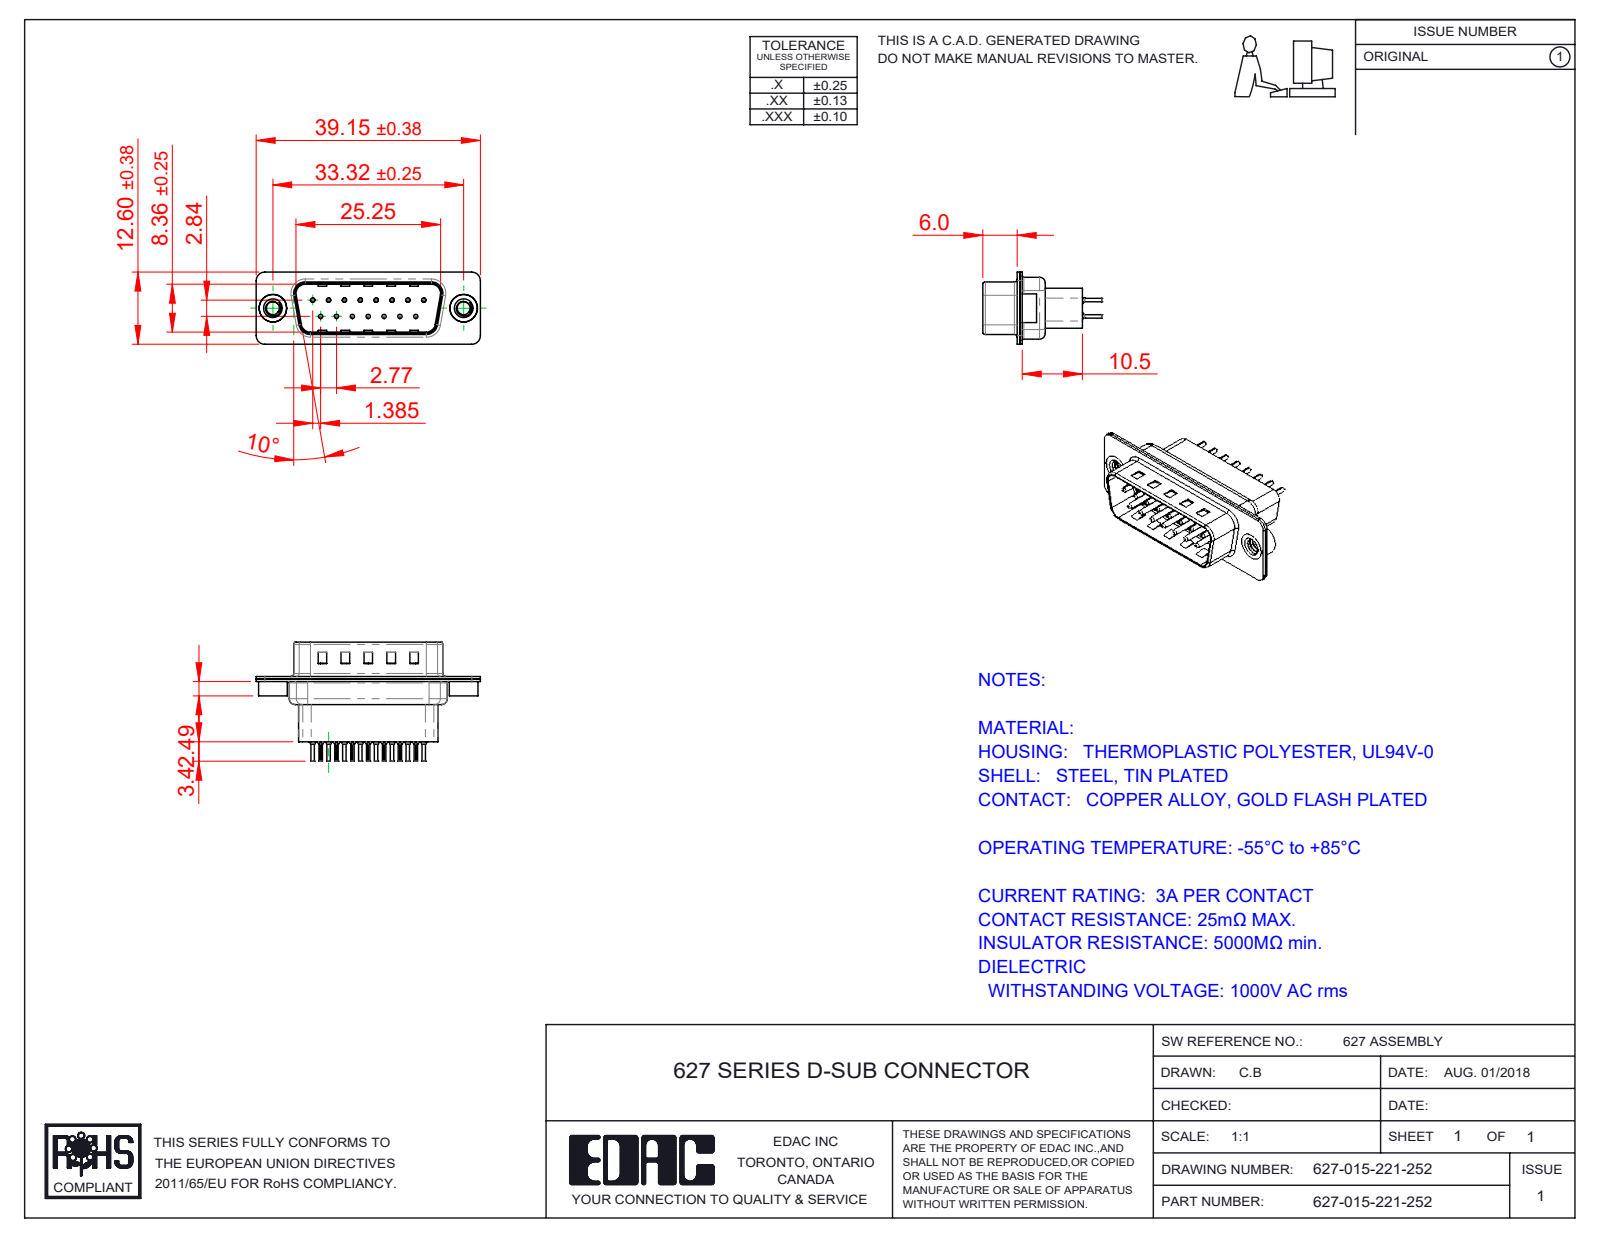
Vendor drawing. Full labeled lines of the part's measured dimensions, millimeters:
Part name (STEP PRODUCT): 627 Contact Row 1_21H; 627 Shell Rear_15 Contacts; 627 4-40 Threaded Rivet; 627 Contact Row 2_21H (+3 more)
STEP written by: SolidWorks 2020 (CONFIG_CONTROL_DESIGN)
Units: millimetres
Bodies: 20 solids, 1806 faces (499 planar, 686 cylindrical, 621 other)
Overall size (bounding box): 39.15 × 20.8 × 12.6
Volume: 2 534 mm³ · Surface area: 6 600 mm²
Round holes (diameter × count): ⌀0.2 ×15, ⌀0.35 ×15, ⌀1.1 ×15, ⌀1.6 ×15, ⌀2.26 ×2, ⌀4 ×2, ⌀4.8 ×2
Round bosses / shafts (diameter × count): ⌀2 ×15, ⌀1.5 ×15, ⌀0.75 ×15, ⌀0.6 ×15, ⌀5 ×2, ⌀4.9 ×2
Partial cylindrical surfaces — rounded edges, fillets, slot ends (radius × count): R0.1 ×30, R1.5 ×16, R2 ×12, R0.5 ×8, R1.6 ×8, R0.25 ×4, R0.6 ×4, R0.65 ×4
Main face-to-face distances: 0.4, 0.45, 0.9, 0.82, 9.58, 1.5, 0.68, 7.68, 1.4, 1.08
Hole centre spacings: 3.16, 2.77, 5.54, 8.31, 11.08, 5.03, 5.04, 7.48
